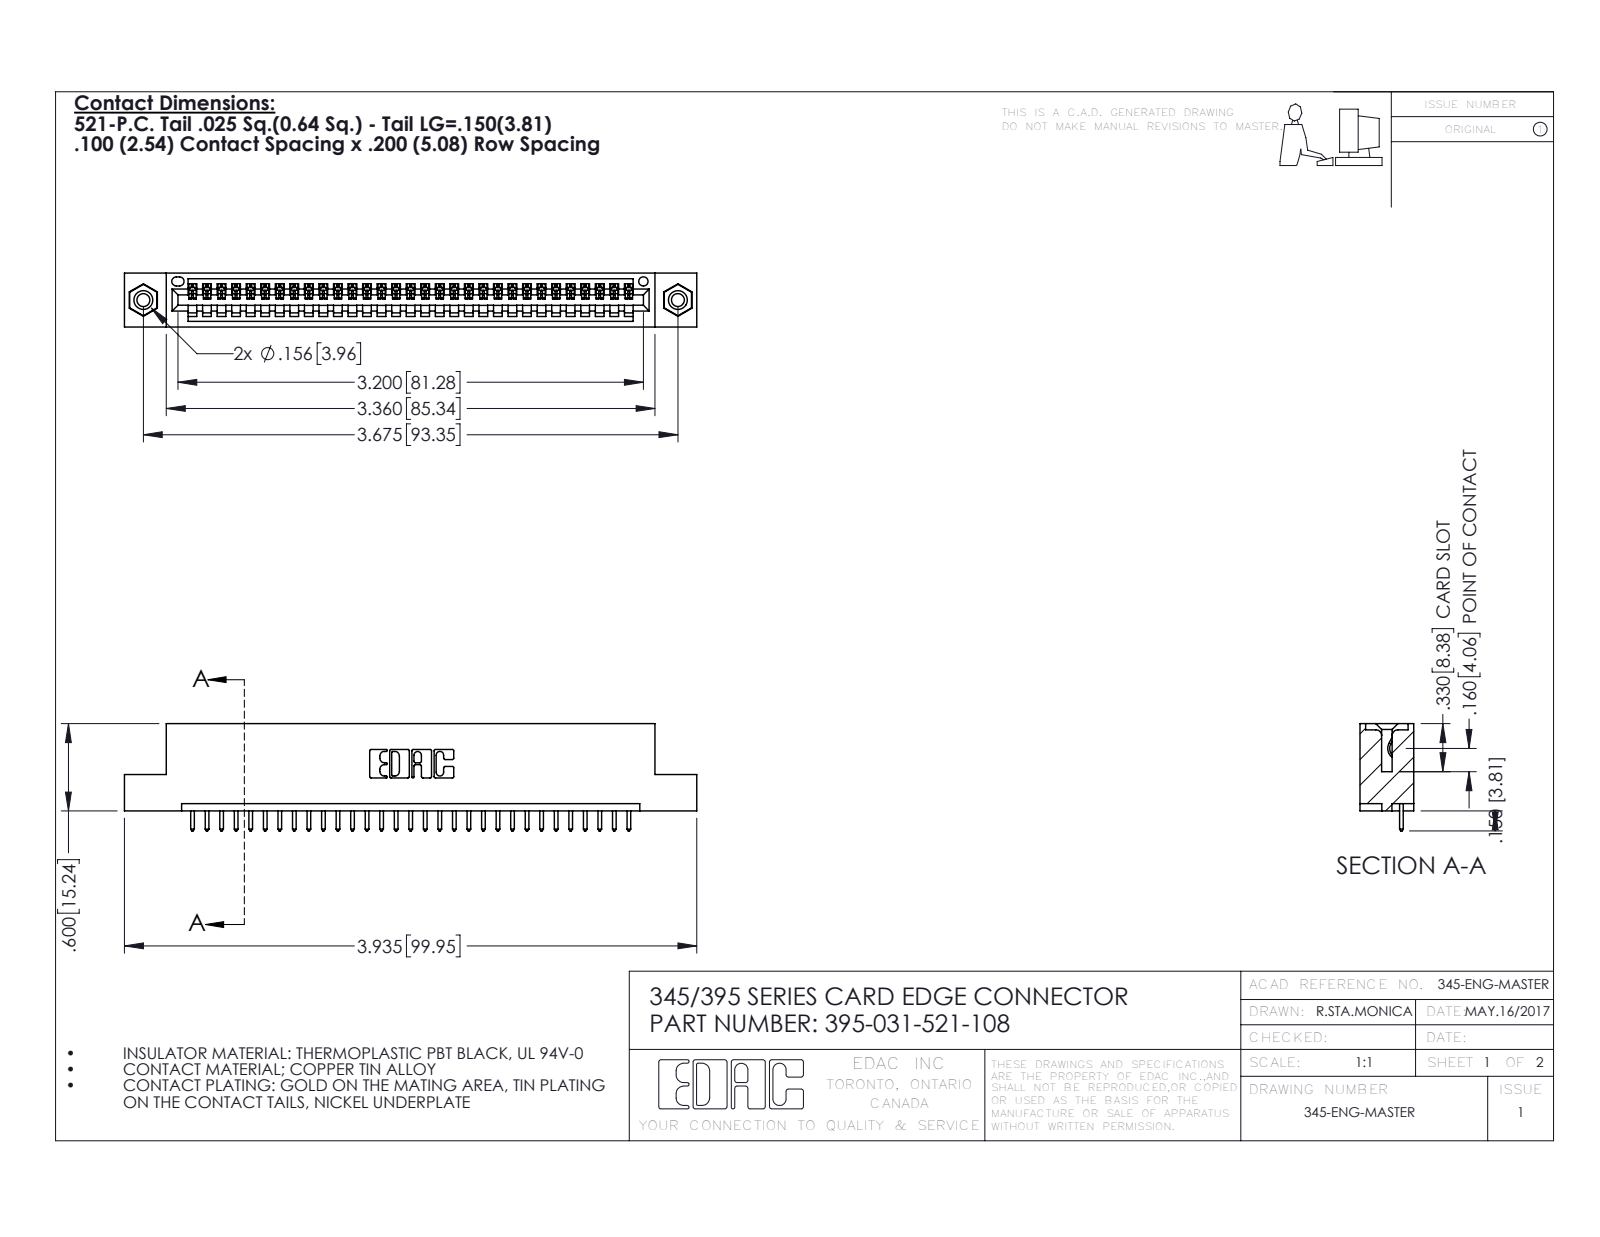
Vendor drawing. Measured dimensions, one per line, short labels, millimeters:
name: 345-292-001_345-293-121; 345-250-001_345-250-003-102; 395-031-521-108; 345 Part_Flush Mounting Lugs - 0.156 Dia-TI
written by: SolidWorks 2016 (CONFIG_CONTROL_DESIGN)
unit: mm
bodies: 34 solids, 1984 faces (1352 planar, 616 cylindrical, 16 other)
size: 99.9 × 18.7 × 9.4
volume: 9 310 mm³; area: 11 900 mm²
holes: 2× ⌀2.3, 2× ⌀3.2, 2× ⌀4, 1× ⌀1.6
bosses: 2× ⌀3.9
rounds: 62× R0.2, 62× R0.3, 22× R0.3, 6× R0.2, 6× R0.8, 3× R0.7, 2× R0.8, 2× R1
face distances: 1.8, 7.6, 5.1, 9.4, 2.5, 6.9, 0.6, 5.7, 3.8, 1.8
hole spacings: 6.9, 87.4, 93.3
